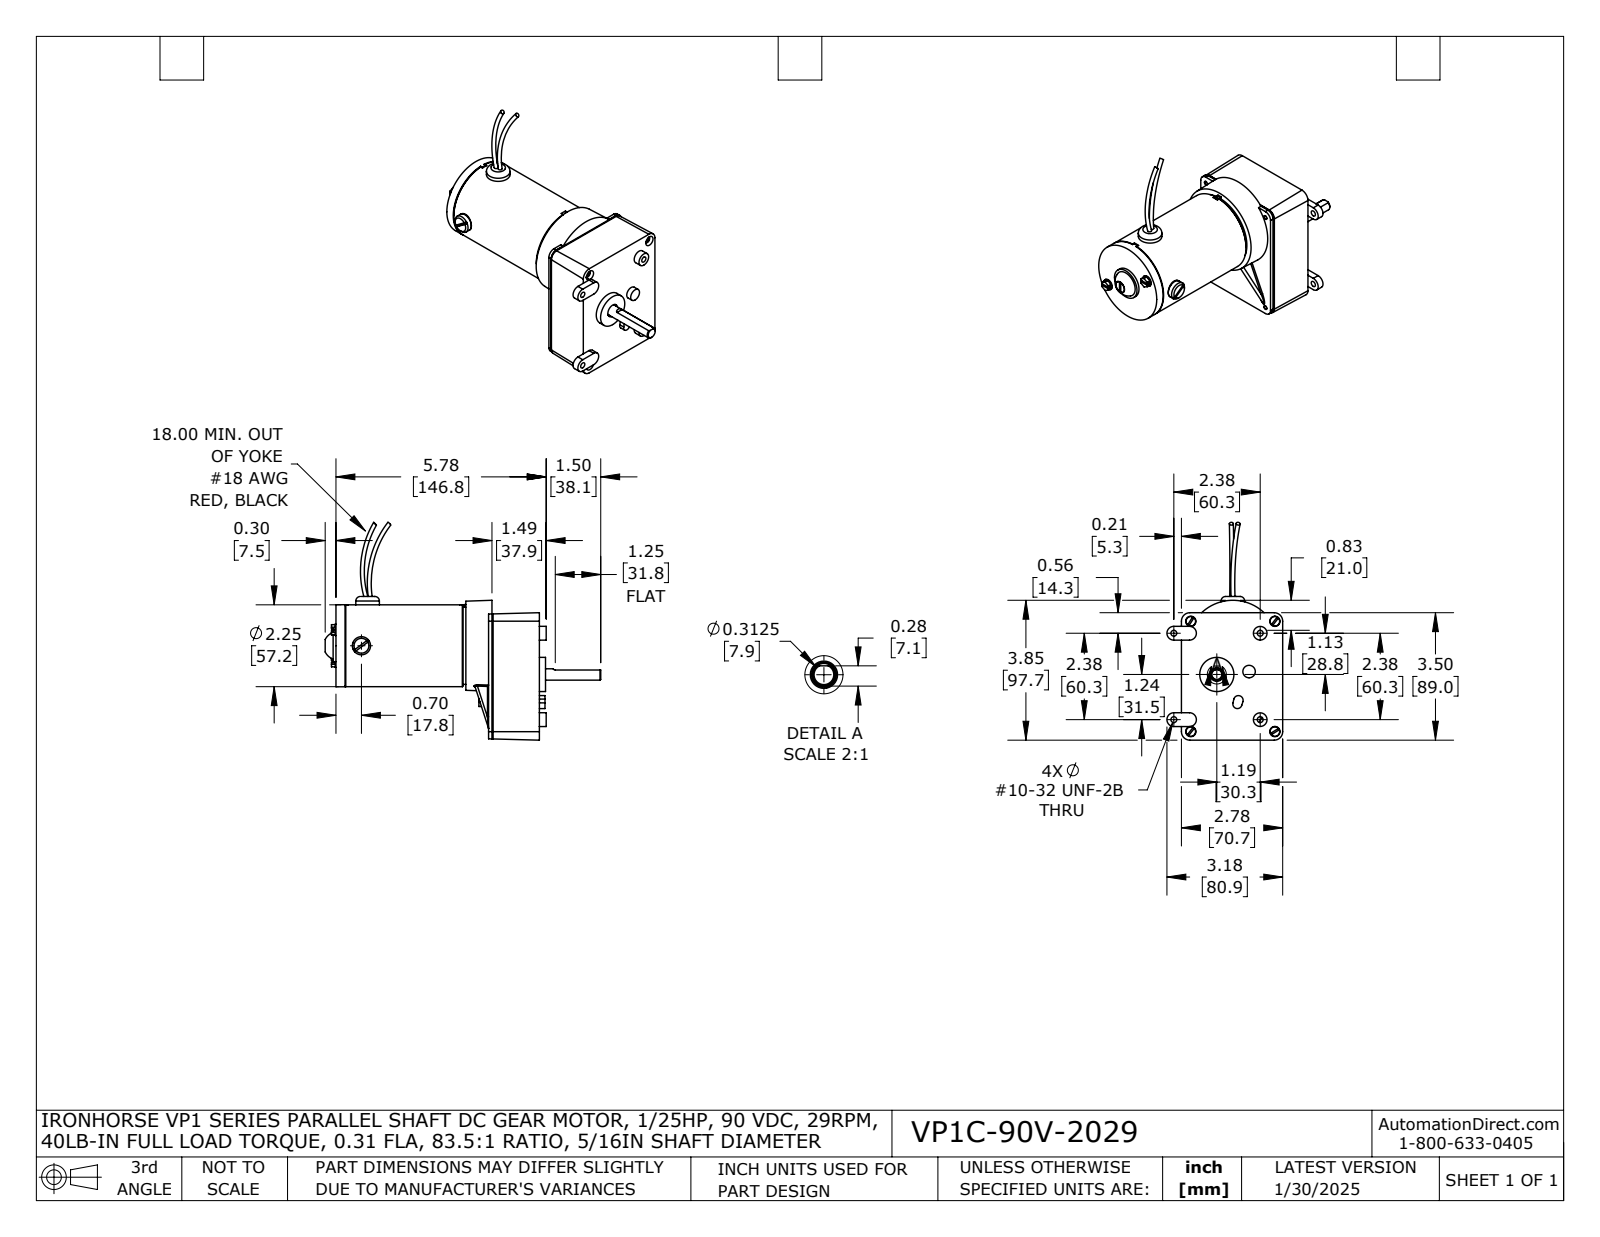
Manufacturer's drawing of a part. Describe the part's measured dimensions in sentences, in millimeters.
The part is named "VP1C-90V-2029". Its 3-D file was written by "SolidWorks 2021 (AUTOMOTIVE_DESIGN)". It is 34 solids with 1338 faces: 477 planar, 580 cylindrical and 281 other. Overall it measures 192.5 by 152.1 by 80.8 millimeters. Its volume is 224 700 cubic millimeters and its surface area 146 200 square millimeters. Round holes: 7 of diameter 7.1, 4 of diameter 0.9, 4 of diameter 3, 4 of diameter 3.8, 4 of diameter 3.8, 4 of diameter 4.1, 2 of diameter 3.2, 2 of diameter 4.7, 1 of diameter 3.2, 1 of diameter 3.2, 1 of diameter 5.4, 1 of diameter 6.1. Round bosses or shafts: 4 of diameter 3.5, 3 of diameter 8, 2 of diameter 9.5, 1 of diameter 57.3, 1 of diameter 57.2, 1 of diameter 53.9, 1 of diameter 50.9, 1 of diameter 50.8. Partial cylindrical surfaces (rounded edges, fillets, slot ends): 24 of radius 0.7, 24 of radius 1.3, 12 of radius 0.5, 12 of radius 1.4, 12 of radius 1.5, 8 of radius 0.8, 8 of radius 0.8, 8 of radius 4.8. The main face-to-face distances are 33.1, 2.5, 30.7, 35.5, 33, 2.4, 32.3, 29.9, 0.8, 3.1. The hole center spacings are 22.2, 19.6, 49.2, 58.7, 58.7, 77, 77, 3.4.
